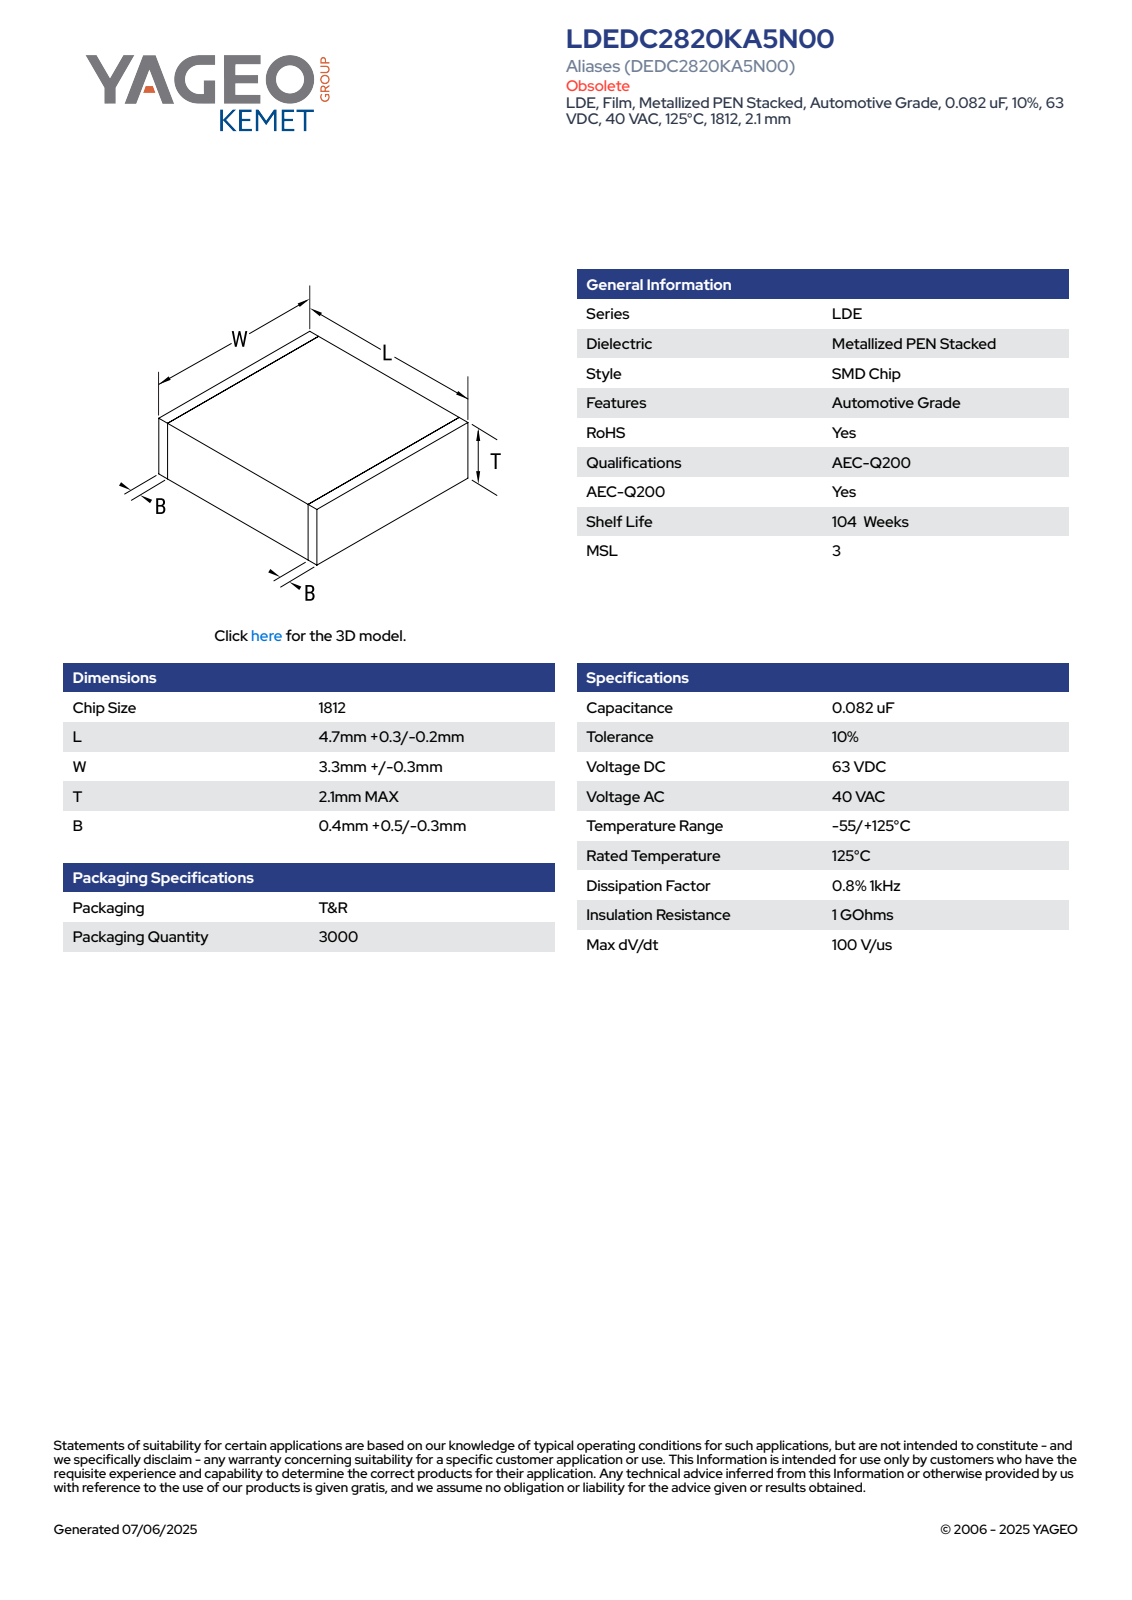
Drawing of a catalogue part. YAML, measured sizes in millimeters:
part_name: "CFS_LDELDB_1812_L5W3.6T2.1B0.9"
step_written_by: "SolidWorks 2020 (AUTOMOTIVE_DESIGN)"
units: millimeters
bodies: {solids: 4, faces: 73, planar: 73, cylindrical: 0, other: 0}
overall_size: [5, 3.6, 2.1]
volume: 37
surface_area: 73
face_to_face_distances: [2.08, 3.58, 5, 2.09, 3.59, 2.1, 3.6, 0.5, 4.5, 4]
